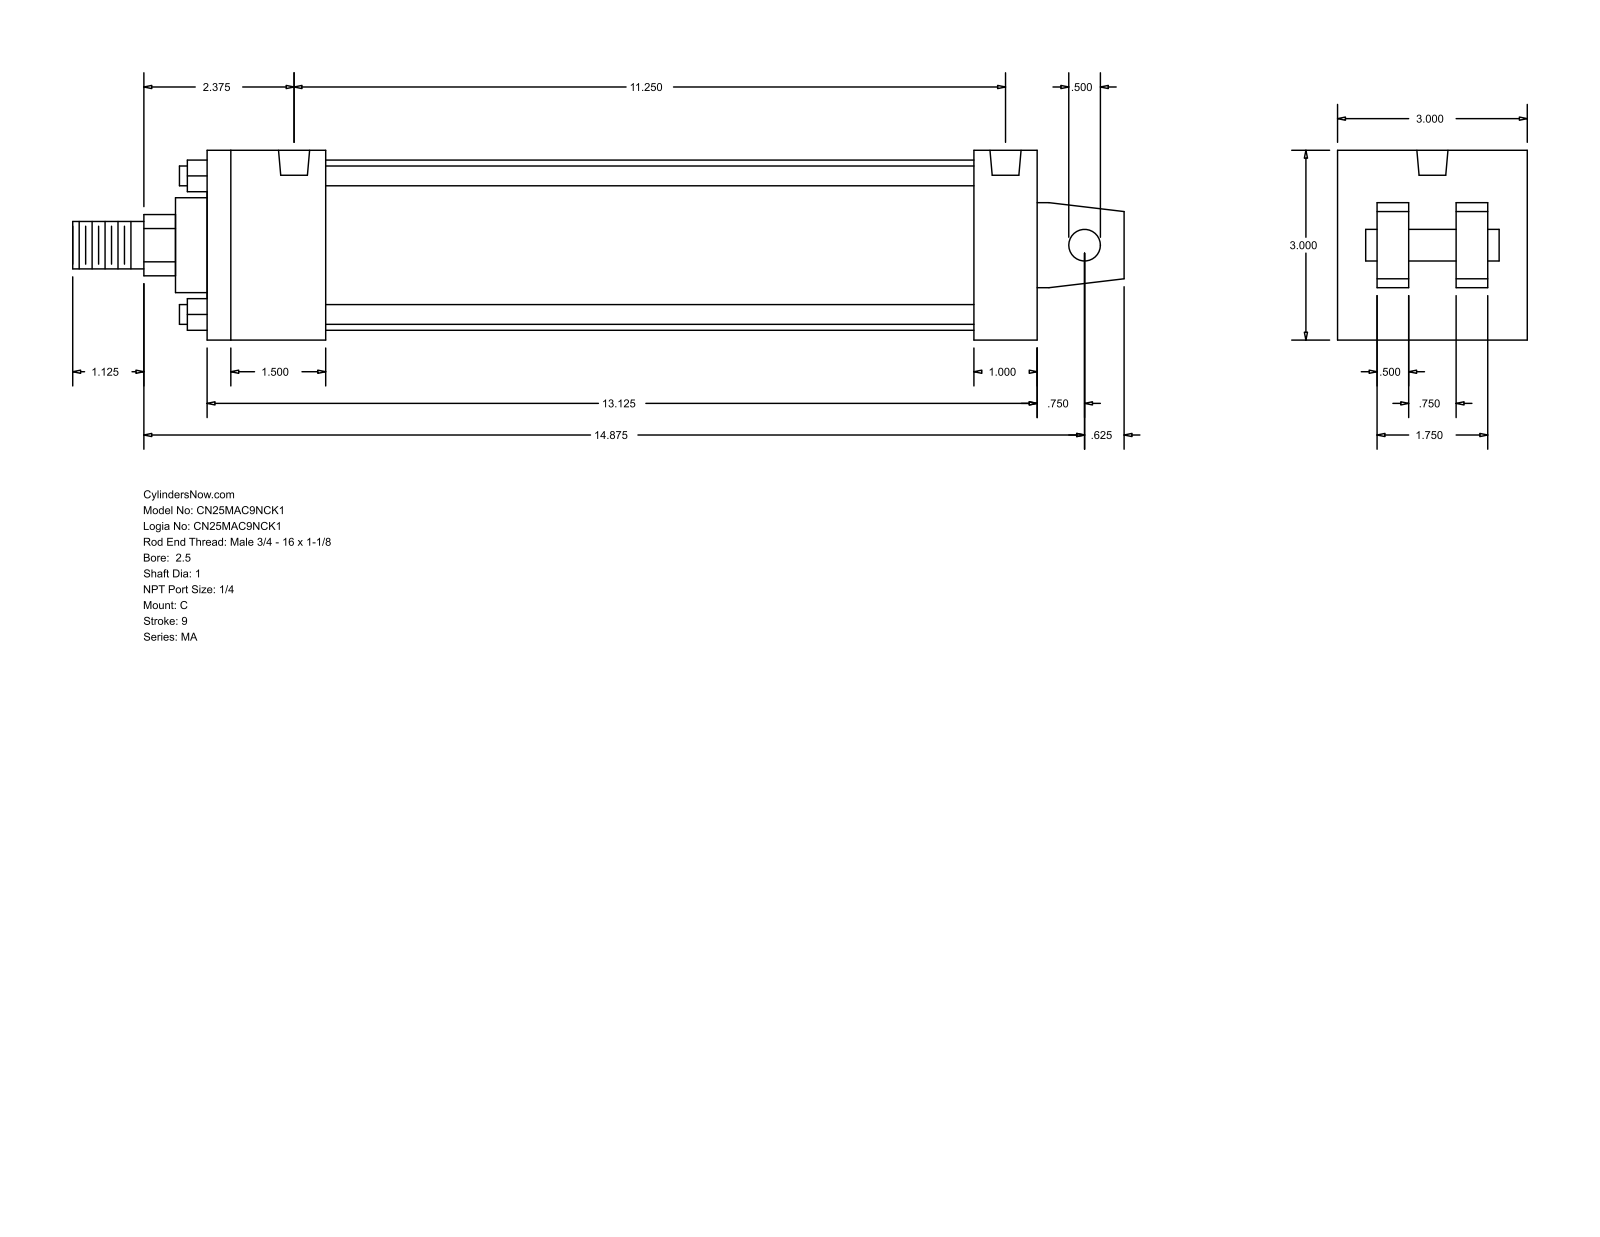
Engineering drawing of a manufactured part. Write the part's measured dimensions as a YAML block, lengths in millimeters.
part_name: "MA_C__0250_1"
step_written_by: "GSSL Pune (CONFIG_CONTROL_DESIGN)"
units: millimeters
bodies: {solids: 0, faces: 103, planar: 76, cylindrical: 27, other: 0}
overall_size: [422.27, 76.2, 76.2]
round_holes:
  - {diameter: 7.94, count: 4}
  - {diameter: 12.49, count: 2}
round_bosses_or_shafts:
  - {diameter: 7.94, count: 4}
  - {diameter: 68.33, count: 1}
  - {diameter: 38.1, count: 1}
  - {diameter: 25.4, count: 1}
  - {diameter: 19.05, count: 1}
  - {diameter: 12.7, count: 1}
partial_cylinders:
  - {radius: 12.29, count: 1}
face_to_face_distances: [76.2, 47.63, 333.37, 12.7, 60.33, 15.87, 28.57, 307.98, 260.35, 285.74]
hole_center_spacings: [285.74]
